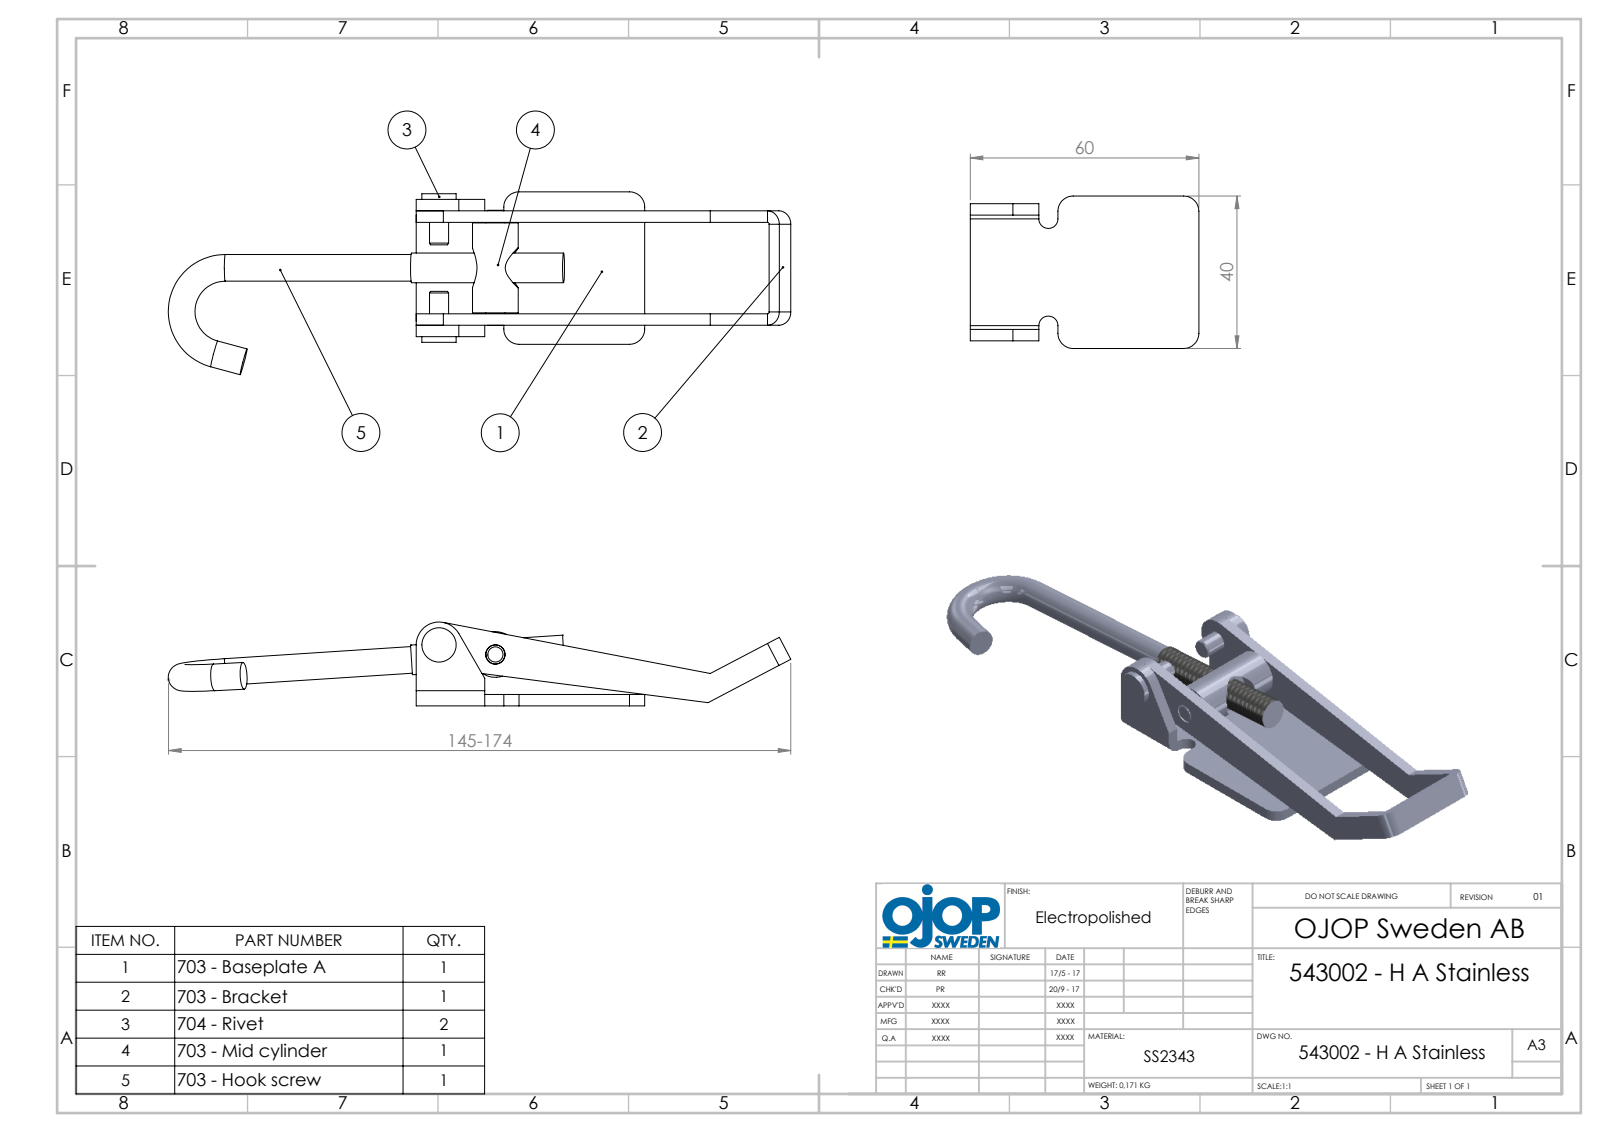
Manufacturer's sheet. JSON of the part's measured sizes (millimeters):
{"part_name": "704 - Rivet Gradin; 703 RF - Bygel; 703 - Platta A RF; 543002 - H A Stainless (+2 more)", "step_written_by": "SolidWorks 2015 (AUTOMOTIVE_DESIGN)", "units": "millimeters", "bodies": {"solids": 6, "faces": 129, "planar": 57, "cylindrical": 58, "other": 14}, "overall_size": [163.4, 47.98, 22], "volume_mm3": 22095, "surface_area_mm2": 16727, "round_holes": [[5.1, 2], [7.2, 2]], "round_bosses_or_shafts": [[7, 3], [5, 2], [12, 1], [9, 1], [7.8, 1]], "partial_cylinders_radius": [[4, 6], [0.5, 2], [1, 2], [2.5, 2], [3.5, 2], [6, 1]], "face_to_face_distances": [3, 27, 30, 24, 6, 33, 36, 5, 2, 8], "hole_center_spacings": [15.01]}
